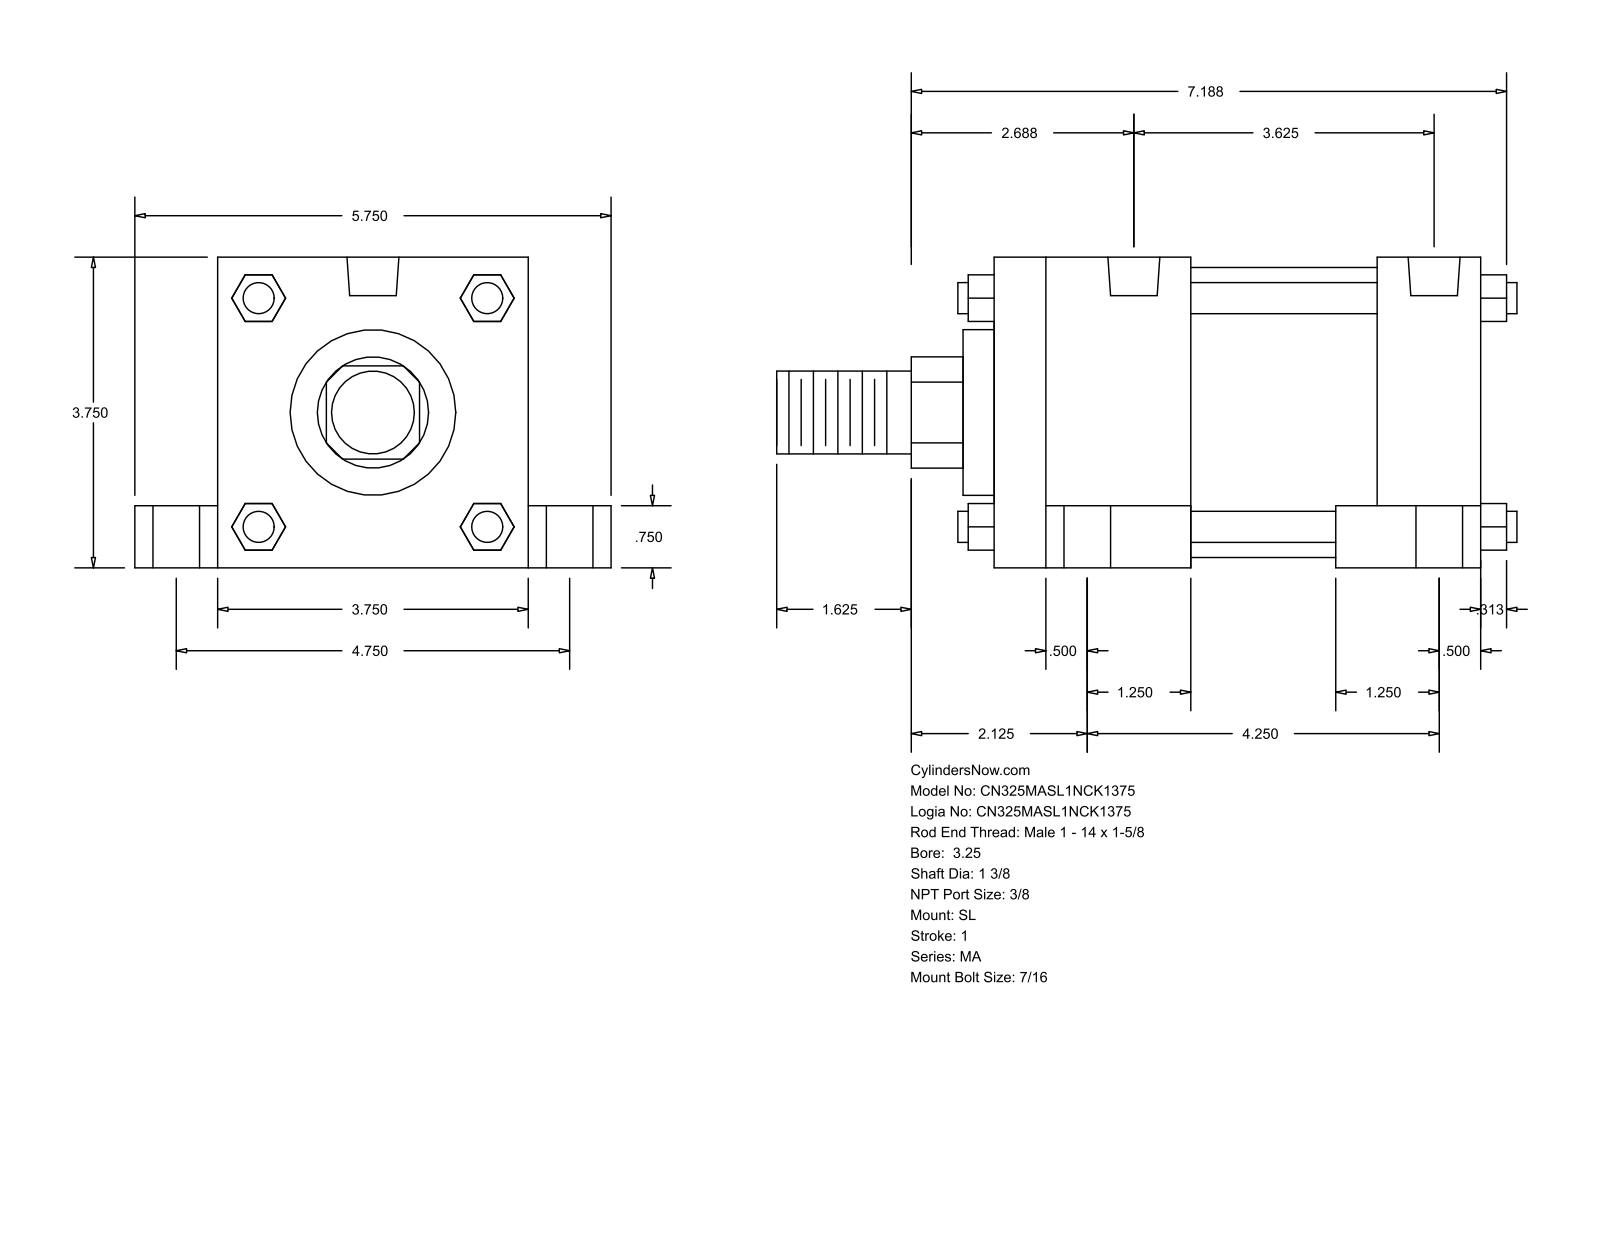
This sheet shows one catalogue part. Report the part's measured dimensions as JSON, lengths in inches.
{"part_name": "MA_SL__0325_1.375", "step_written_by": "GSSL Pune (CONFIG_CONTROL_DESIGN)", "units": "inches", "bodies": {"solids": 0, "faces": 148, "planar": 112, "cylindrical": 36, "other": 0}, "overall_size": [8.937, 5.75, 3.75], "round_holes": [[0.437, 4], [0.563, 4], [0.813, 4], [0.627, 2]], "round_bosses_or_shafts": [[0.375, 4], [3.5, 1], [2, 1], [1.375, 1], [1, 1]], "partial_cylinders_radius": [[0.672, 1]], "face_to_face_distances": [3.75, 5.875, 1, 4.75, 4.625, 1.25, 2.375, 2.25, 3.5, 0.75], "hole_center_spacings": [0.188, 2.376, 2.388, 2.441, 2.491, 3.25, 3.437, 4.23]}
